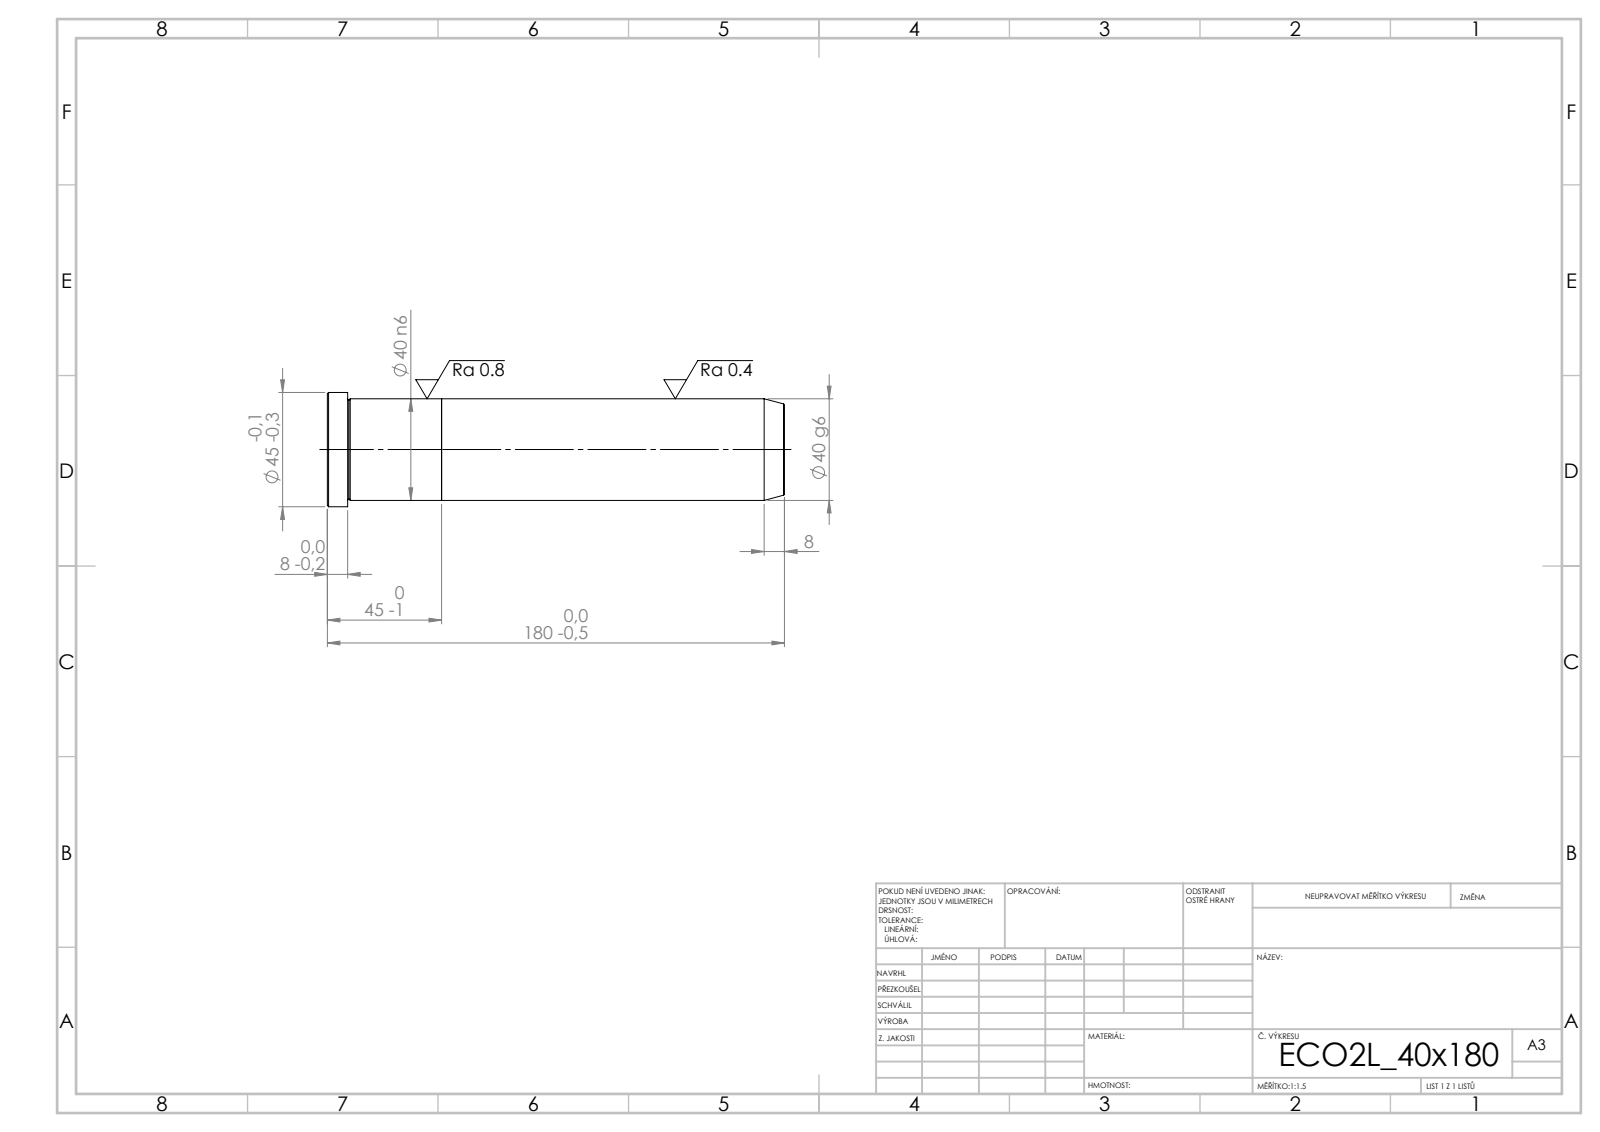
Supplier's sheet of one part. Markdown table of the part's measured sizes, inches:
| quantity | value |
| --- | --- |
| STEP written by | SolidWorks 2019 (CONFIG_CONTROL_DESIGN) |
| units | inches |
| bodies | 2 solids, 21 faces (5 planar, 6 cylindrical, 10 other) |
| overall size | 7.087 × 1.772 × 1.772 |
| volume | 13.9 in³ |
| surface area | 43.68 in² |
| round bosses / shafts (diameter × count) | 1.772 × 1, 1.575 × 1 |
| main face-to-face distances | 1.772, 5.315, 7.087, 6.772, 1.457, 0.315 |
